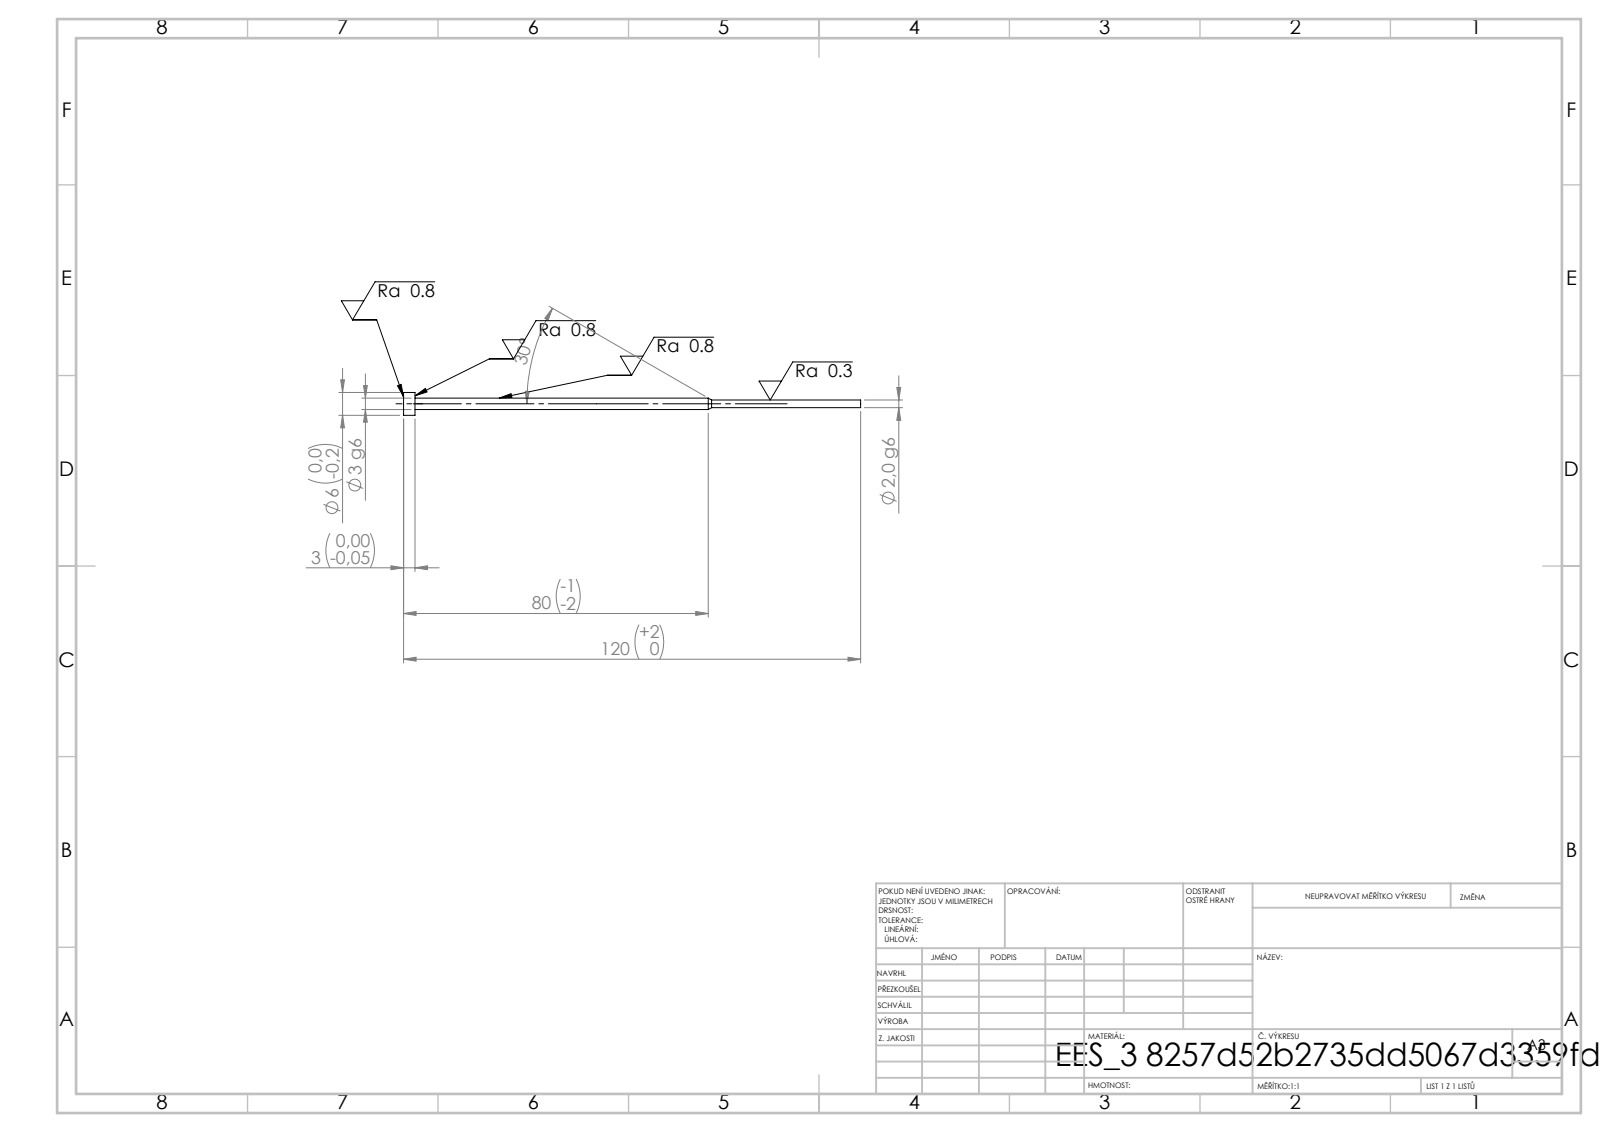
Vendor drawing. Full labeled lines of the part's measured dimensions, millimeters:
STEP written by: SolidWorks 2019 (CONFIG_CONTROL_DESIGN)
Units: millimetres
Bodies: 1 solid, 11 faces (3 planar, 6 cylindrical, 2 other)
Overall size (bounding box): 120 × 6 × 6
Volume: 756 mm³ · Surface area: 1 089 mm²
Round bosses / shafts (diameter × count): ⌀6 ×1, ⌀3 ×1, ⌀2 ×1
Main face-to-face distances: 3, 117, 120
